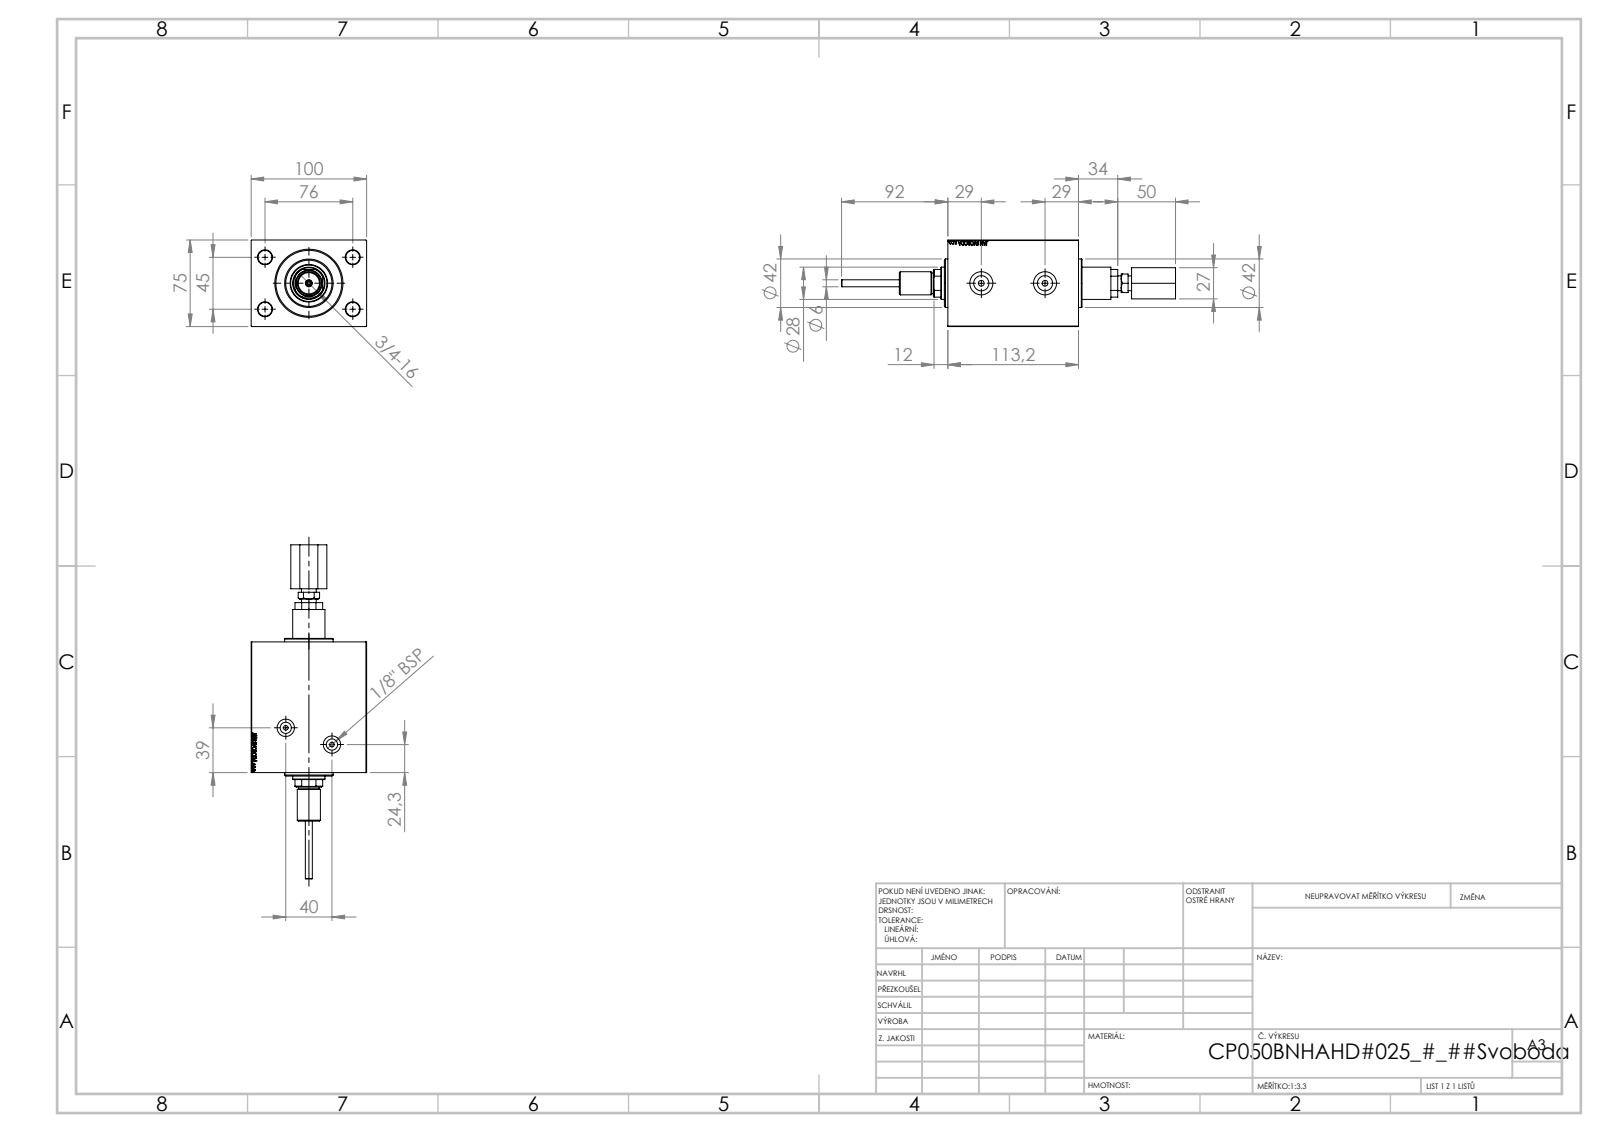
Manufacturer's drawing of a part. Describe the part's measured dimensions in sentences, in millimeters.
The part is named "V450DCP_VC_B; V450DCP_B_RodCooling_ACCESSORIES; V450CP_MALE_METRIC; V450DCP_B_Body (+1 more)". Its 3-D file was written by "SolidWorks 2019 (CONFIG_CONTROL_DESIGN)". It is 5 solids with 986 faces: 438 planar, 98 cylindrical and 450 other. Overall it measures 289.2 by 100 by 75 millimeters. Its volume is 849 226 cubic millimeters and its surface area 132 636 square millimeters. Round holes: 4 of diameter 12, 2 of diameter 4, 2 of diameter 5, 2 of diameter 9.73, 2 of diameter 13.16, 2 of diameter 15, 2 of diameter 20, 1 of diameter 3, 1 of diameter 6, 1 of diameter 18.5, 1 of diameter 28, 1 of diameter 31.5. Round bosses or shafts: 1 of diameter 42, 1 of diameter 20, 1 of diameter 18, 1 of diameter 12.78. Partial cylindrical surfaces (rounded edges, fillets, slot ends): 1 of radius 13.5. The main face-to-face distances are 75, 100, 113.2, 14, 99.2, 13, 43, 1, 27, 112.2. The hole center spacings are 44.16, 45, 76, 88.32, 42.55, 55.2.
